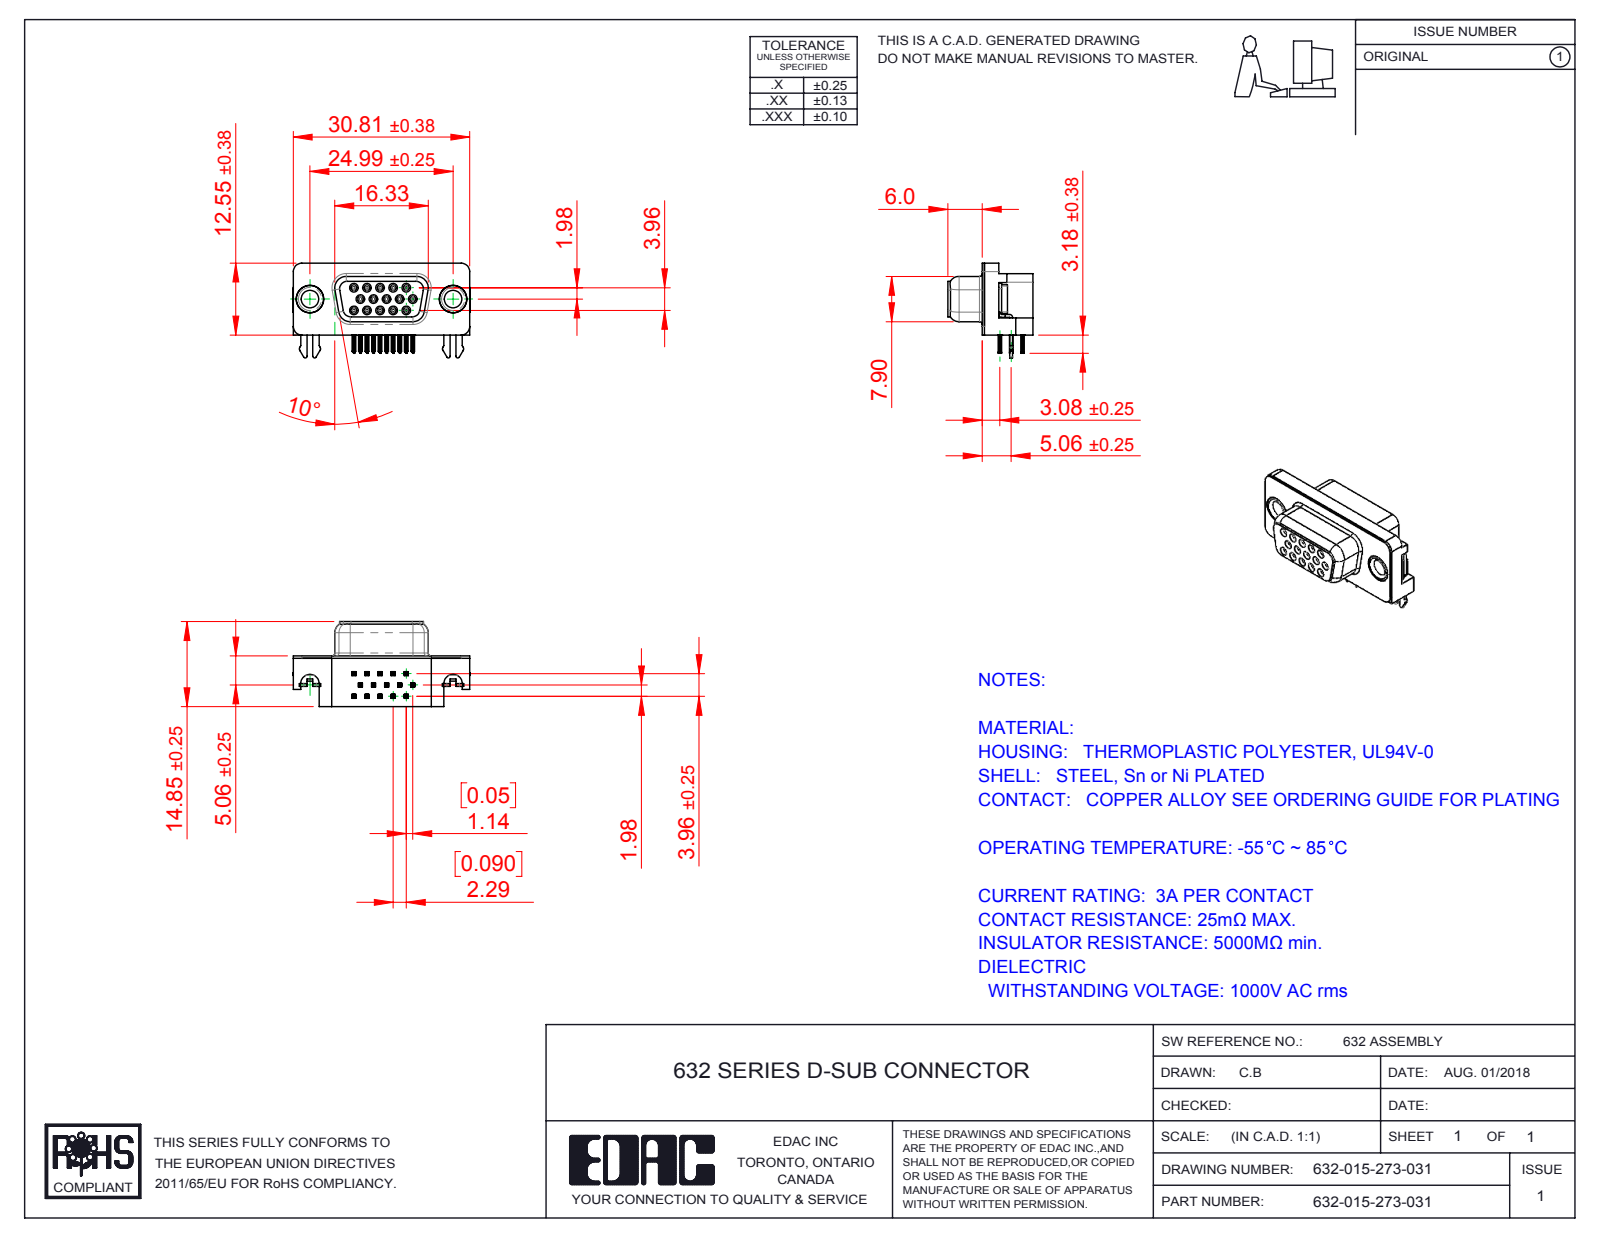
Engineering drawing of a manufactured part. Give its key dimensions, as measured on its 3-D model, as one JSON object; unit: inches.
{"part_name": "632 2 Prong Board Lock; 632 Contact Middle_Recessed; 632 Thru Hole Rivet; 632 Contact Bottom (+5 more)", "step_written_by": "SolidWorks 2016 (CONFIG_CONTROL_DESIGN)", "units": "inches", "bodies": {"solids": 21, "faces": 2298, "planar": 990, "cylindrical": 594, "other": 714}, "overall_size": [1.216, 0.652, 0.585], "volume_in3": 0.177, "surface_area_in2": 7.736, "round_holes": [[0.031, 15], [0.035, 15], [0.12, 2], [0.157, 2], [0.189, 2], [0.197, 2]], "round_bosses_or_shafts": [[0.047, 15], [0.193, 2], [0.187, 2], [0.152, 2]], "partial_cylinders_radius": [[0.004, 120], [0.006, 60], [0.014, 30], [0.013, 15], [0.039, 11], [0.011, 10], [0.02, 10], [0.01, 8]], "face_to_face_distances": [0.016, 0.078, 0.333, 0.348, 0.114, 0.098, 0.234, 0.252, 0.264, 0.278], "hole_center_spacings": [0.09, 0.09, 0.156, 0.18, 0.238, 0.156, 0.18, 0.27]}
